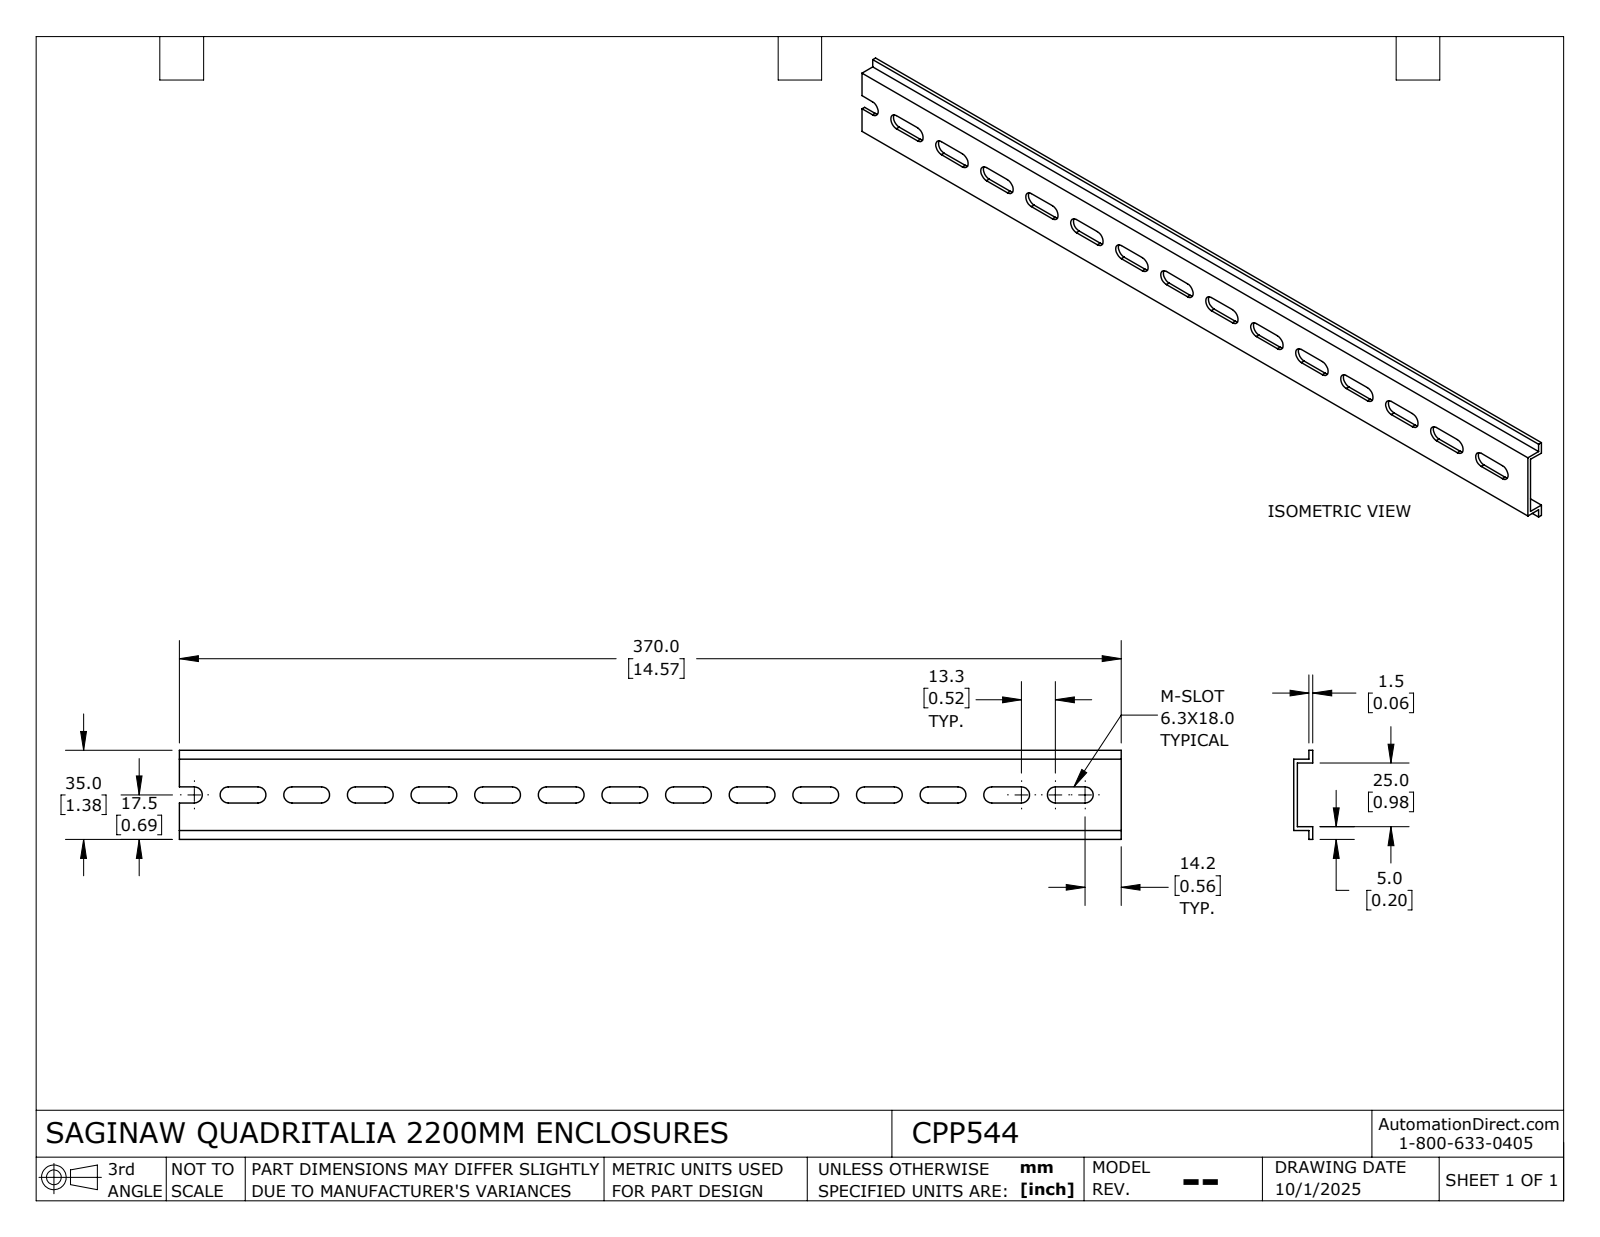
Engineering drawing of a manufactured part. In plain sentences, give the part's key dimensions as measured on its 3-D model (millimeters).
The part is named "CPP544_Default". Its 3-D file was written by "SolidWorks 2024 (CONFIG_CONTROL_DESIGN)". It is 1 solid with 74 faces: 45 planar, 29 cylindrical and 0 other. Overall it measures 370 by 35 by 7.5 millimeters. Its volume is 23 804 cubic millimeters and its surface area 33 919 square millimeters. Partial cylindrical surfaces (rounded edges, fillets, slot ends): 29 of radius 3.15. The main face-to-face distances are 1.5, 6, 26.5, 7.5, 4.5, 28, 25, 3.5, 5, 30.
